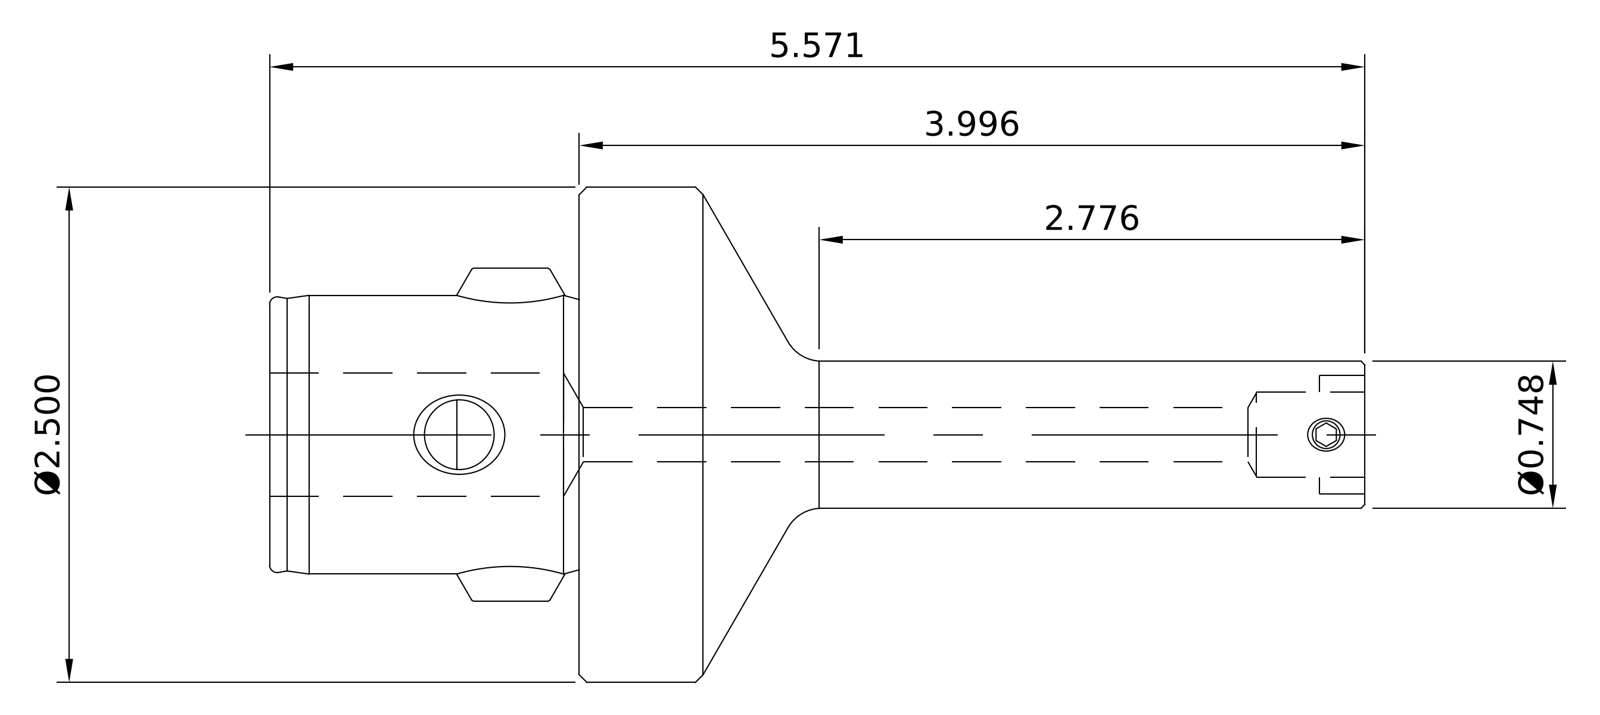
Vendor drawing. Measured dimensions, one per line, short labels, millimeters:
name: 11.332.610
written by: SolidWorks 2014 (AUTOMOTIVE_DESIGN)
unit: mm
bodies: 1 solid, 108 faces (21 planar, 36 cylindrical, 51 other)
size: 141.5 × 63.27 × 63.27
volume: 102 097 mm³; area: 24 044 mm²
holes: 1× ⌀3.3, 1× ⌀4.2, 1× ⌀5, 1× ⌀9, 1× ⌀10, 1× ⌀11, 1× ⌀11.5, 1× ⌀14, 1× ⌀16, 1× ⌀18.5
bosses: 1× ⌀63.27, 1× ⌀36, 1× ⌀19, 1× ⌀18.6
rounds: 2× R1.5, 1× R18
face distances: 40, 141.5, 101.5, 3, 37, 138.5, 9.34, 135.6, 132.6, 95.6
hole spacings: 13.5, 111.95
